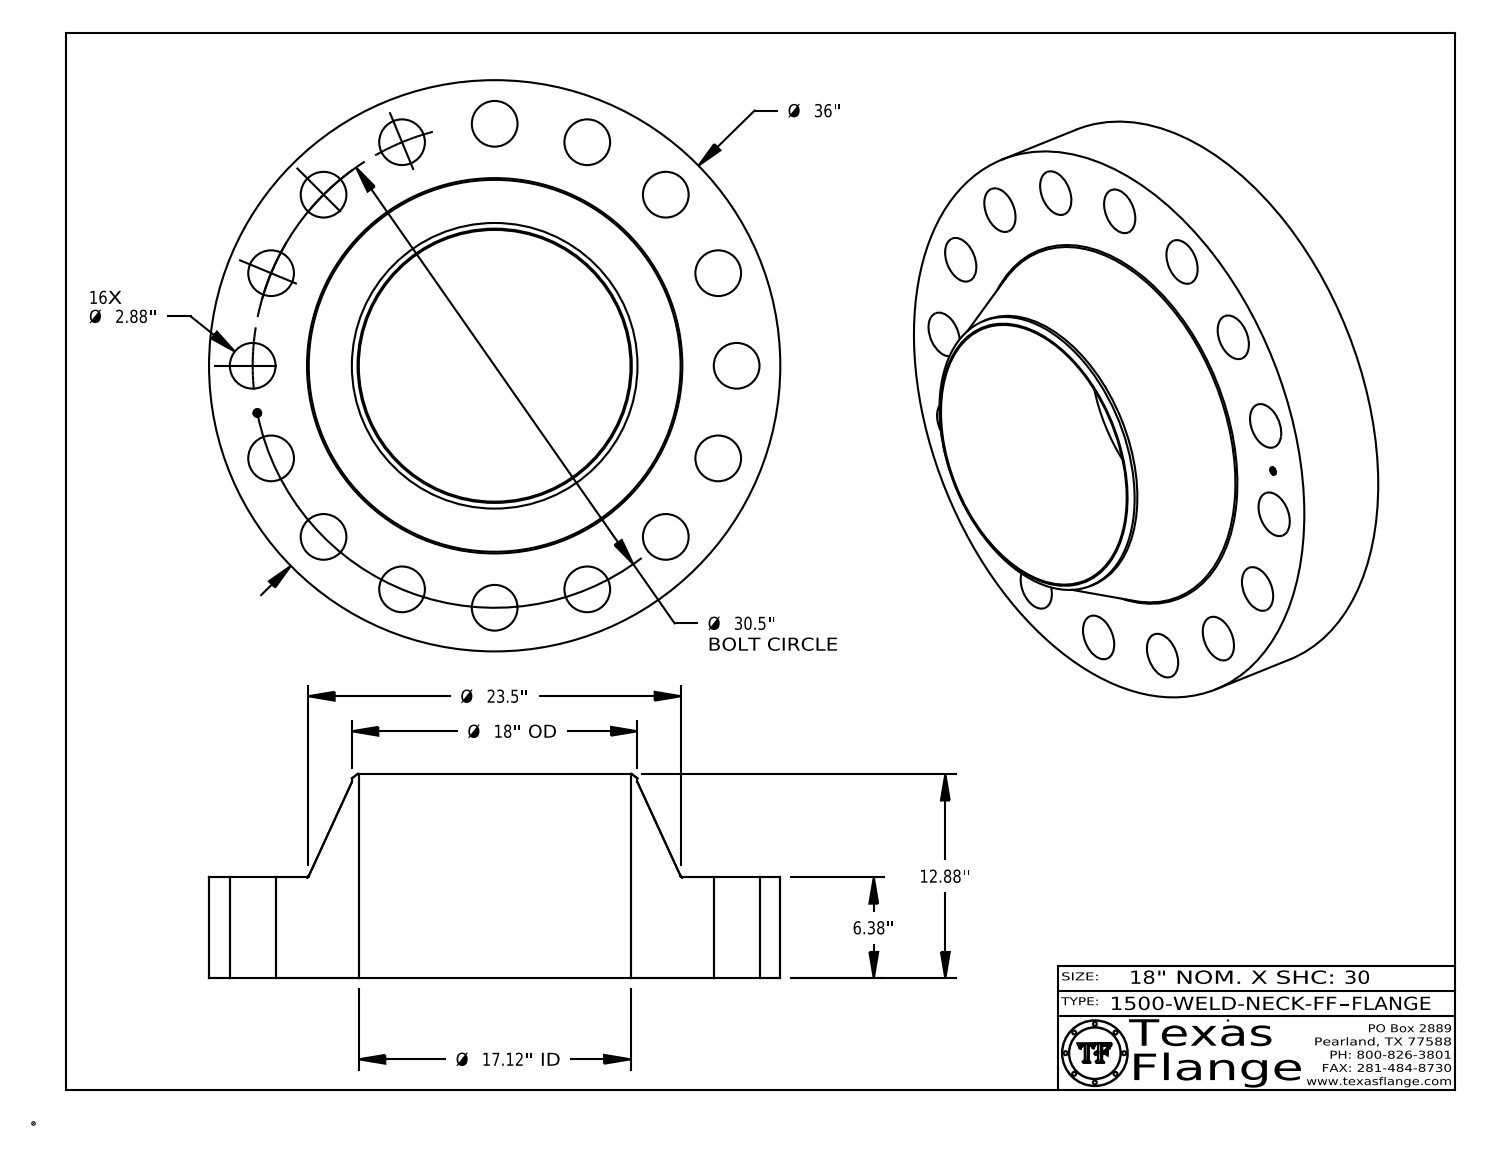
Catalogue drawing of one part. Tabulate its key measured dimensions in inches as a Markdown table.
| quantity | value |
| --- | --- |
| part name | 1500-WELD-NECK-FF |
| STEP written by | CATIA V5 STEP AP214 (AUTOMOTIVE_DESIGN) |
| units | inches |
| bodies | 1 solid, 432 faces (368 planar, 58 cylindrical, 6 other) |
| overall size | 36 × 36 × 12.88 |
| volume | 5 027 in³ |
| surface area | 3 972 in² |
| round holes (diameter × count) | 2.88 × 16, 0.495 × 1, 17.124 × 1 |
| round bosses / shafts (diameter × count) | 0.03 × 8, 36 × 1, 18 × 1, 0.39 × 1 |
| main face-to-face distances | 6.38, 12.88, 6.5, 6.365, 0.015, 6.515, 0.148, 0.145, 0.027, 0.096 |
| hole center spacings | 5.95, 16.945, 29.914, 15.25, 11.672, 11.672, 15.25, 21.567 |
